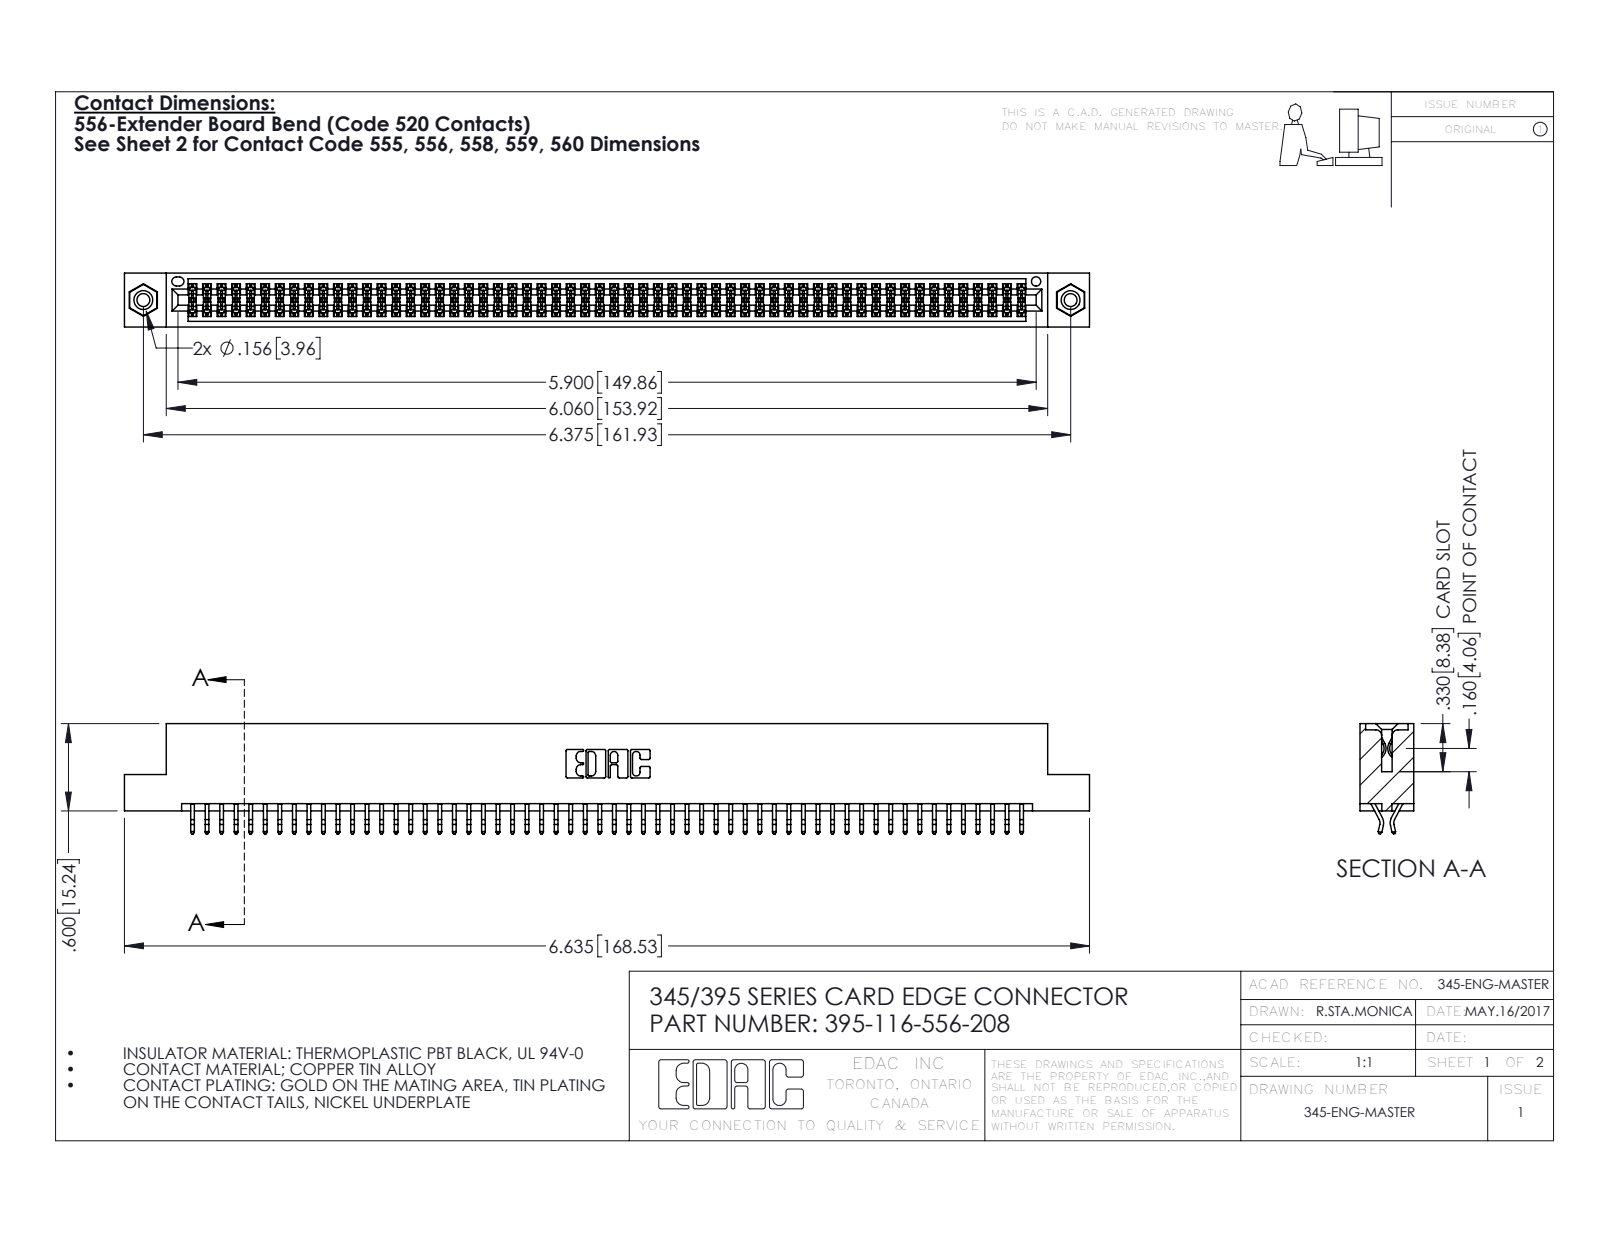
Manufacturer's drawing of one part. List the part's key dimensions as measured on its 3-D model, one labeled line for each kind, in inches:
Part name (STEP PRODUCT): 395-116-556-208; 345 Part_Flush Mounting Lugs - 0.156 Dia-TI; 345-250-001_345-250-003-102; 345-292-001_556 Tail
STEP written by: SolidWorks 2016 (CONFIG_CONTROL_DESIGN)
Units: inches
Bodies: 119 solids, 6682 faces (4404 planar, 2262 cylindrical, 16 other)
Overall size (bounding box): 6.635 × 0.757 × 0.37
Volume: 1.007 in³ · Surface area: 38.17 in²
Round holes (diameter × count): ⌀0.089 ×2, ⌀0.125 ×2, ⌀0.156 ×2, ⌀0.064 ×1
Round bosses / shafts (diameter × count): ⌀0.155 ×2
Partial cylindrical surfaces — rounded edges, fillets, slot ends (radius × count): R0.006 ×174, R0.01 ×22, R0.007 ×6, R0.031 ×6, R0.026 ×3, R0.01 ×2, R0.014 ×2, R0.019 ×2
Main face-to-face distances: 0.072, 0.298, 0.37, 0.2, 0.025, 0.098, 0.272, 0.225, 0.175, 0.149
Hole centre spacings: 0.27, 6.139, 6.375
